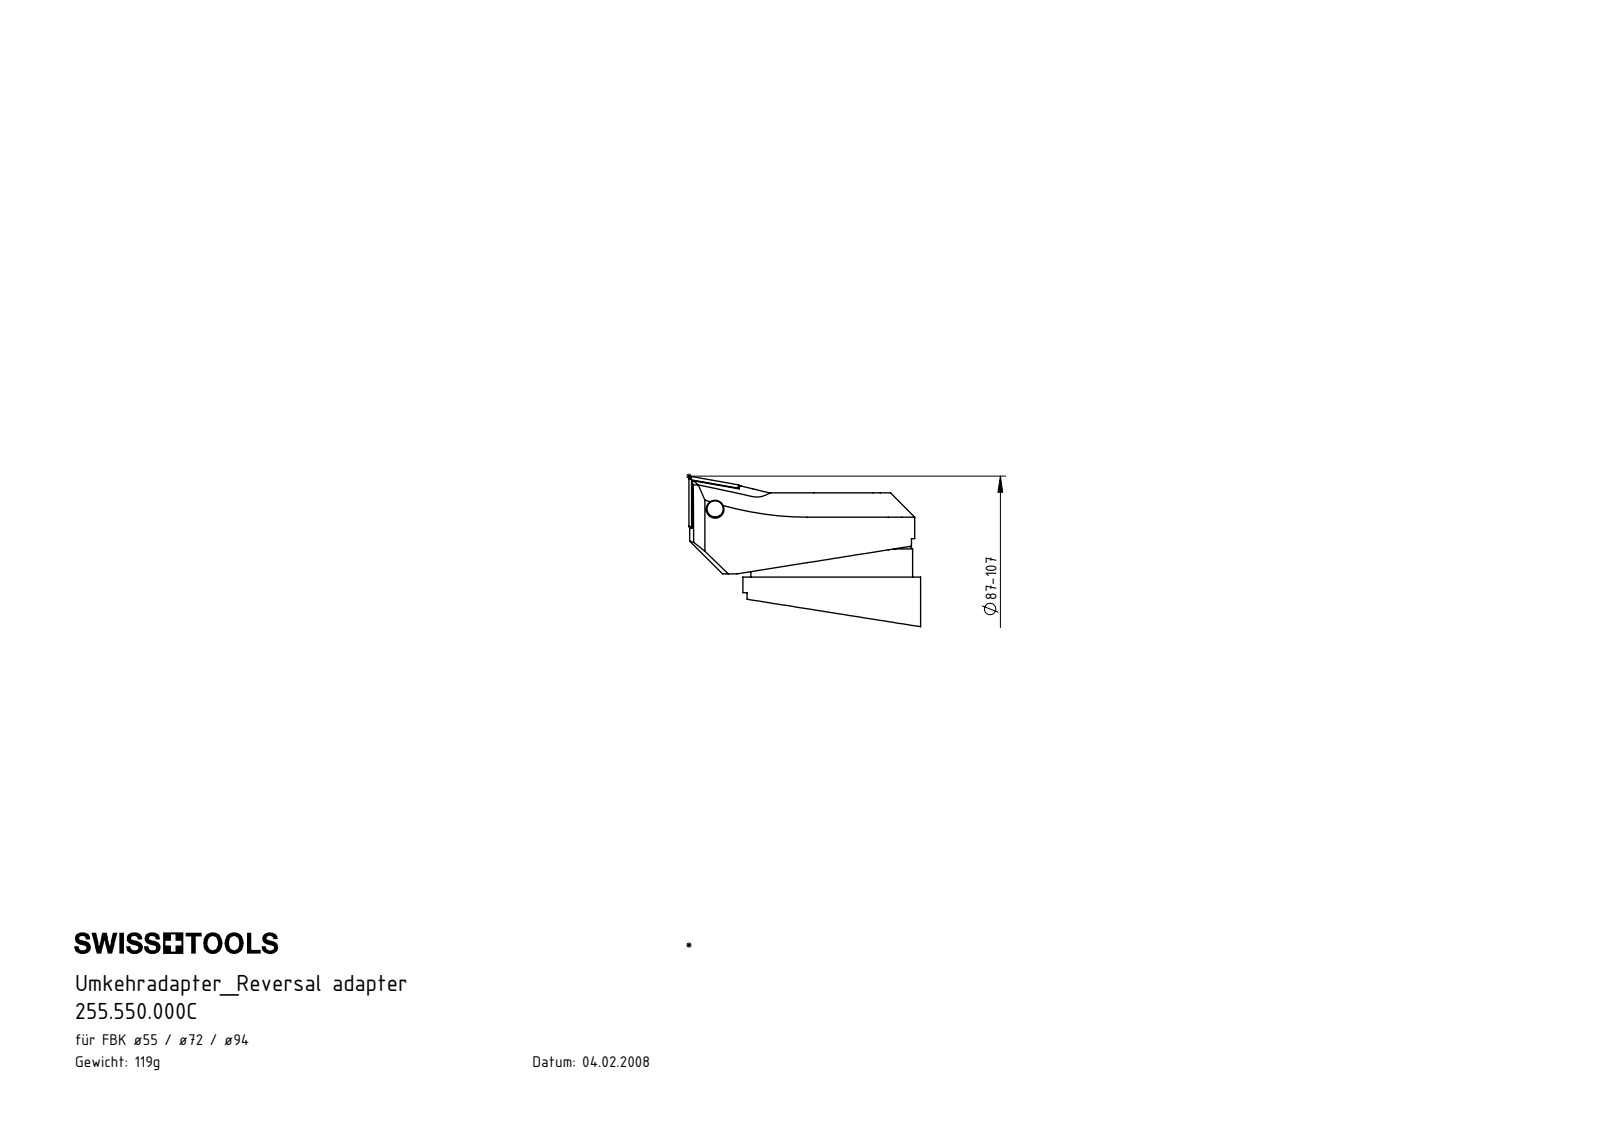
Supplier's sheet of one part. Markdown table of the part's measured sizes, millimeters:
| quantity | value |
| --- | --- |
| part name | F55-U00.001.010_B; 255.550.000C |
| STEP written by | SolidWorks 2017 (CONFIG_CONTROL_DESIGN) |
| units | millimeters |
| bodies | 1 solid, 29 faces (13 planar, 11 cylindrical, 5 other) |
| overall size | 33 × 33 × 15.53 |
| volume | 6 971 mm³ |
| surface area | 3 290 mm² |
| round holes (diameter × count) | 11 × 1, 30 × 1 |
| round bosses / shafts (diameter × count) | 33 × 1 |
| partial cylindrical surfaces (radius × count) | 0.5 × 2 |
| main face-to-face distances | 10, 5.6, 4.4, 8.5, 2.9, 1.5, 0.7, 6.3, 9.2, 10.7 |
